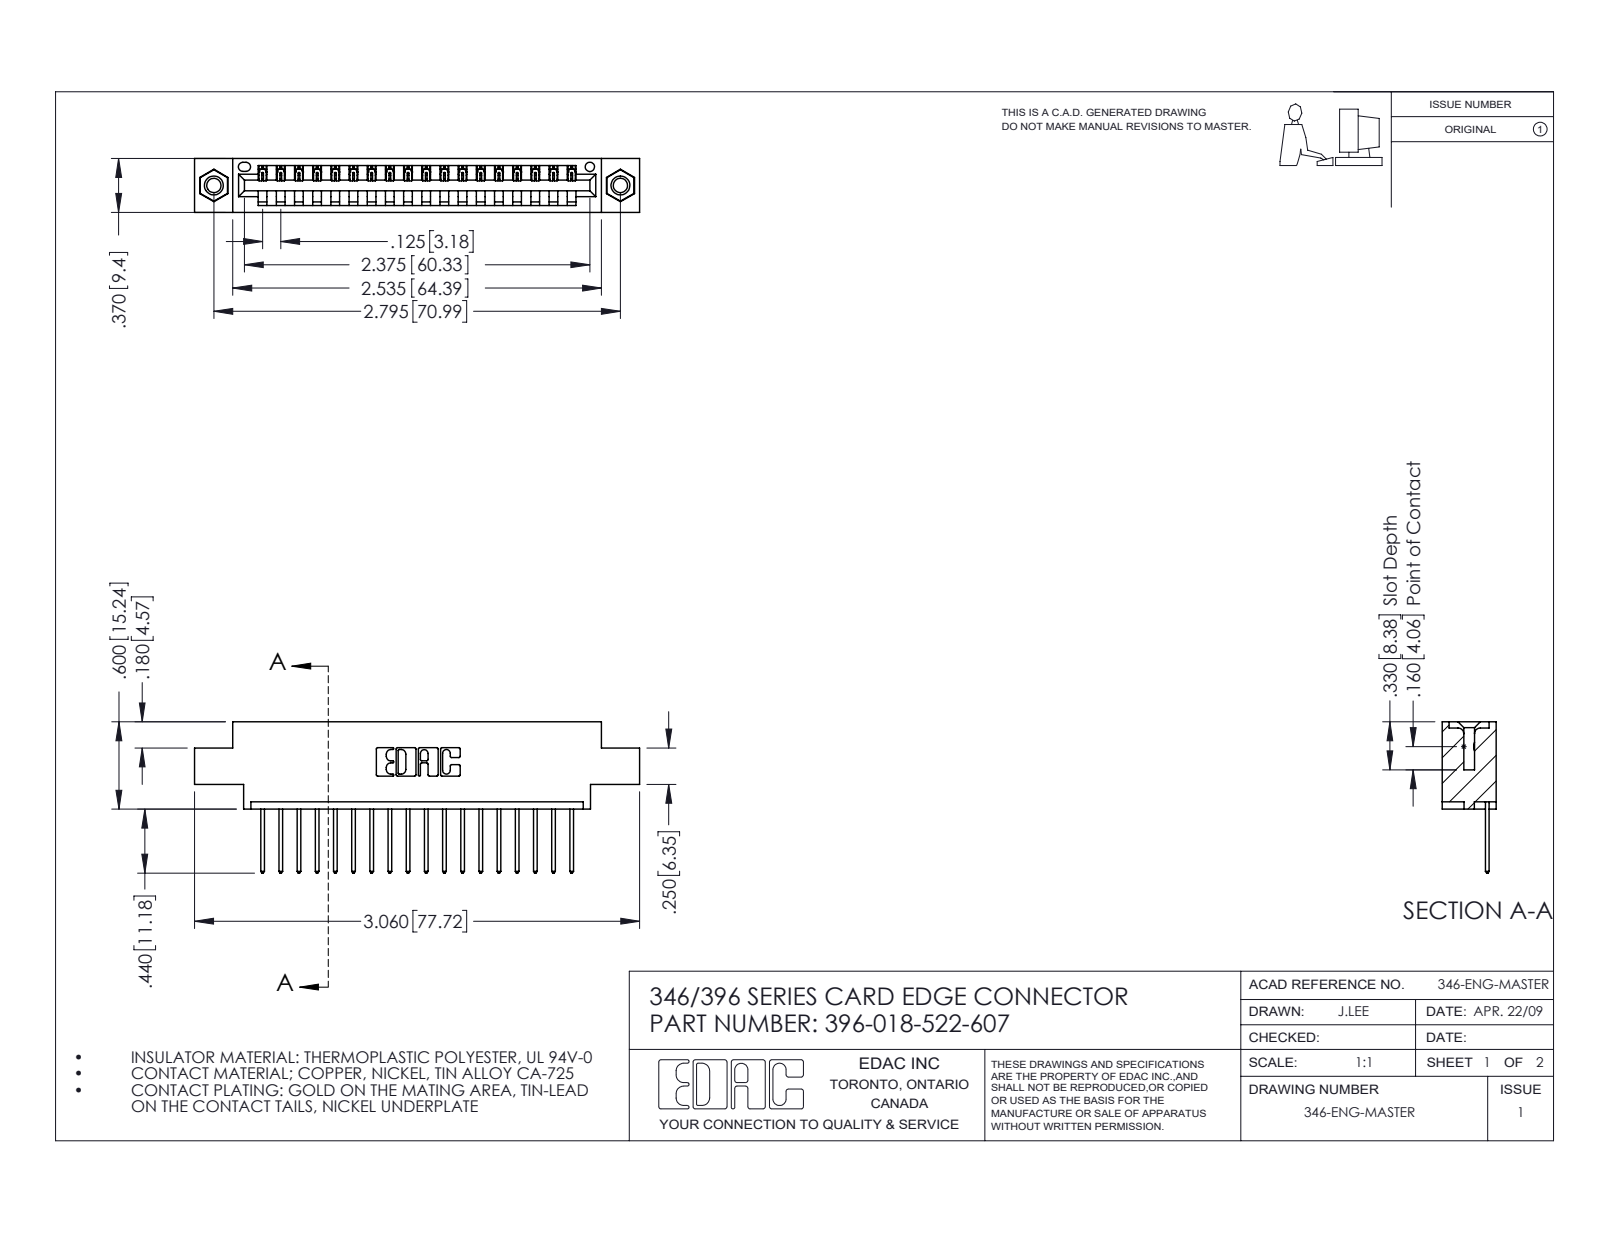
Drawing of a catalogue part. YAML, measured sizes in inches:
part_name: "345-292-001_345-293-122; 396-018-522-607; 345-250-001_345-250-005-103; 346 Part_0.170 Offset - 0.156 Dia-TI"
step_written_by: "SolidWorks 2016 (CONFIG_CONTROL_DESIGN)"
units: inches
bodies: {solids: 21, faces: 1230, planar: 832, cylindrical: 382, other: 16}
overall_size: [3.06, 1.04, 0.37]
volume: 0.434
surface_area: 13.78
round_holes:
  - {diameter: 0.098, count: 2}
  - {diameter: 0.125, count: 2}
  - {diameter: 0.156, count: 2}
  - {diameter: 0.064, count: 1}
round_bosses_or_shafts:
  - {diameter: 0.155, count: 2}
partial_cylinders:
  - {radius: 0.006, count: 36}
  - {radius: 0.01, count: 36}
  - {radius: 0.01, count: 22}
  - {radius: 0.007, count: 6}
  - {radius: 0.031, count: 6}
  - {radius: 0.026, count: 3}
  - {radius: 0.031, count: 2}
  - {radius: 0.04, count: 2}
face_to_face_distances: [0.048, 0.322, 0.37, 0.25, 0.072, 0.298, 0.025, 0.222, 0.148, 0.1]
hole_center_spacings: [0.246, 2.588, 2.795]
